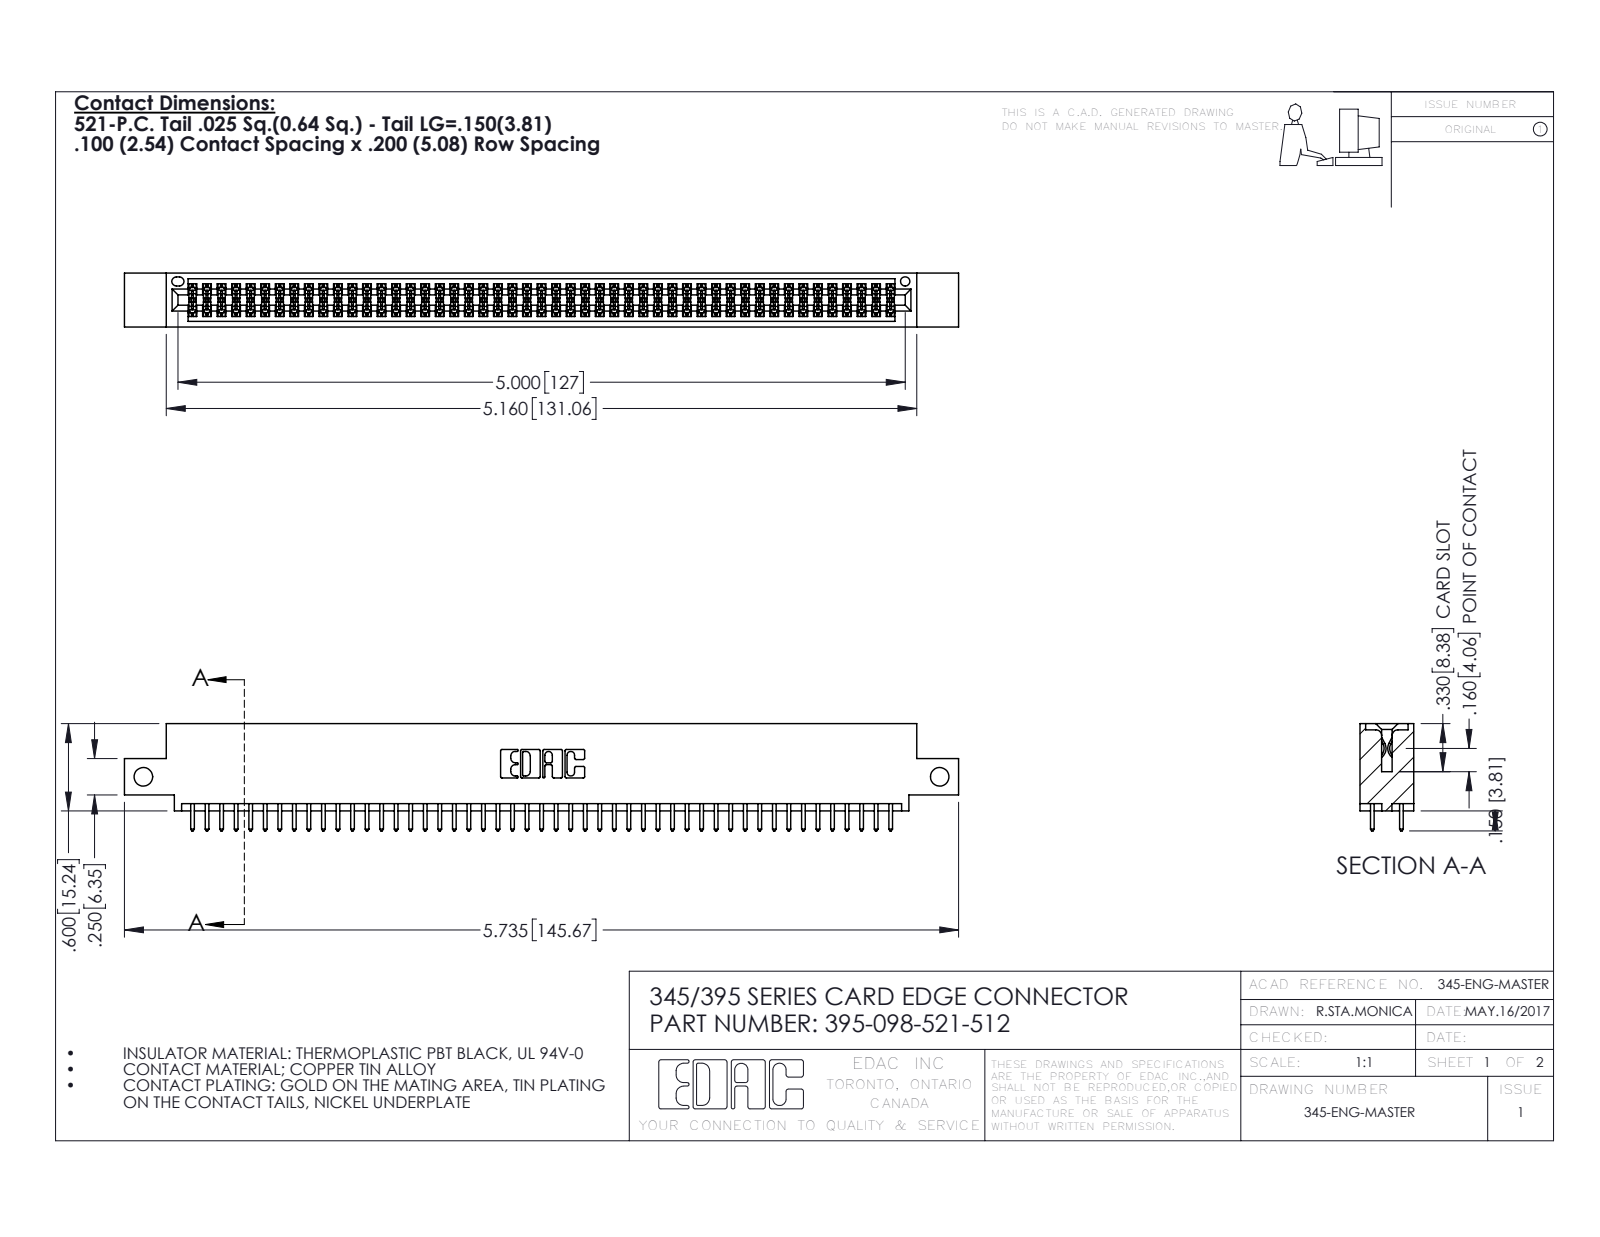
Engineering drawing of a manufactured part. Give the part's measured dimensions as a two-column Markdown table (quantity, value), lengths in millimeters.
| quantity | value |
| --- | --- |
| part name | 345-292-001_345-293-121; 395-098-521-512; 345 Part_0.110 Offset - Side Mount |
| STEP written by | SolidWorks 2016 (CONFIG_CONTROL_DESIGN) |
| units | millimeters |
| bodies | 99 solids, 5030 faces (3318 planar, 1712 cylindrical, 0 other) |
| overall size | 145.7 × 18.7 × 9.4 |
| volume | 14 000 mm³ |
| surface area | 20 550 mm² |
| round holes (diameter × count) | 3.3 × 2, 1.6 × 1 |
| partial cylindrical surfaces (radius × count) | 0.2 × 147, 0.3 × 98, 0.3 × 22, 0.2 × 6, 0.8 × 6, 0.7 × 3, 0.4 × 2, 0.5 × 2 |
| main face-to-face distances | 7.6, 1.8, 5.1, 2.5, 6.9, 0.6, 9.4, 5.7, 4.4, 3.8 |
| hole center spacings | 139.1 |
